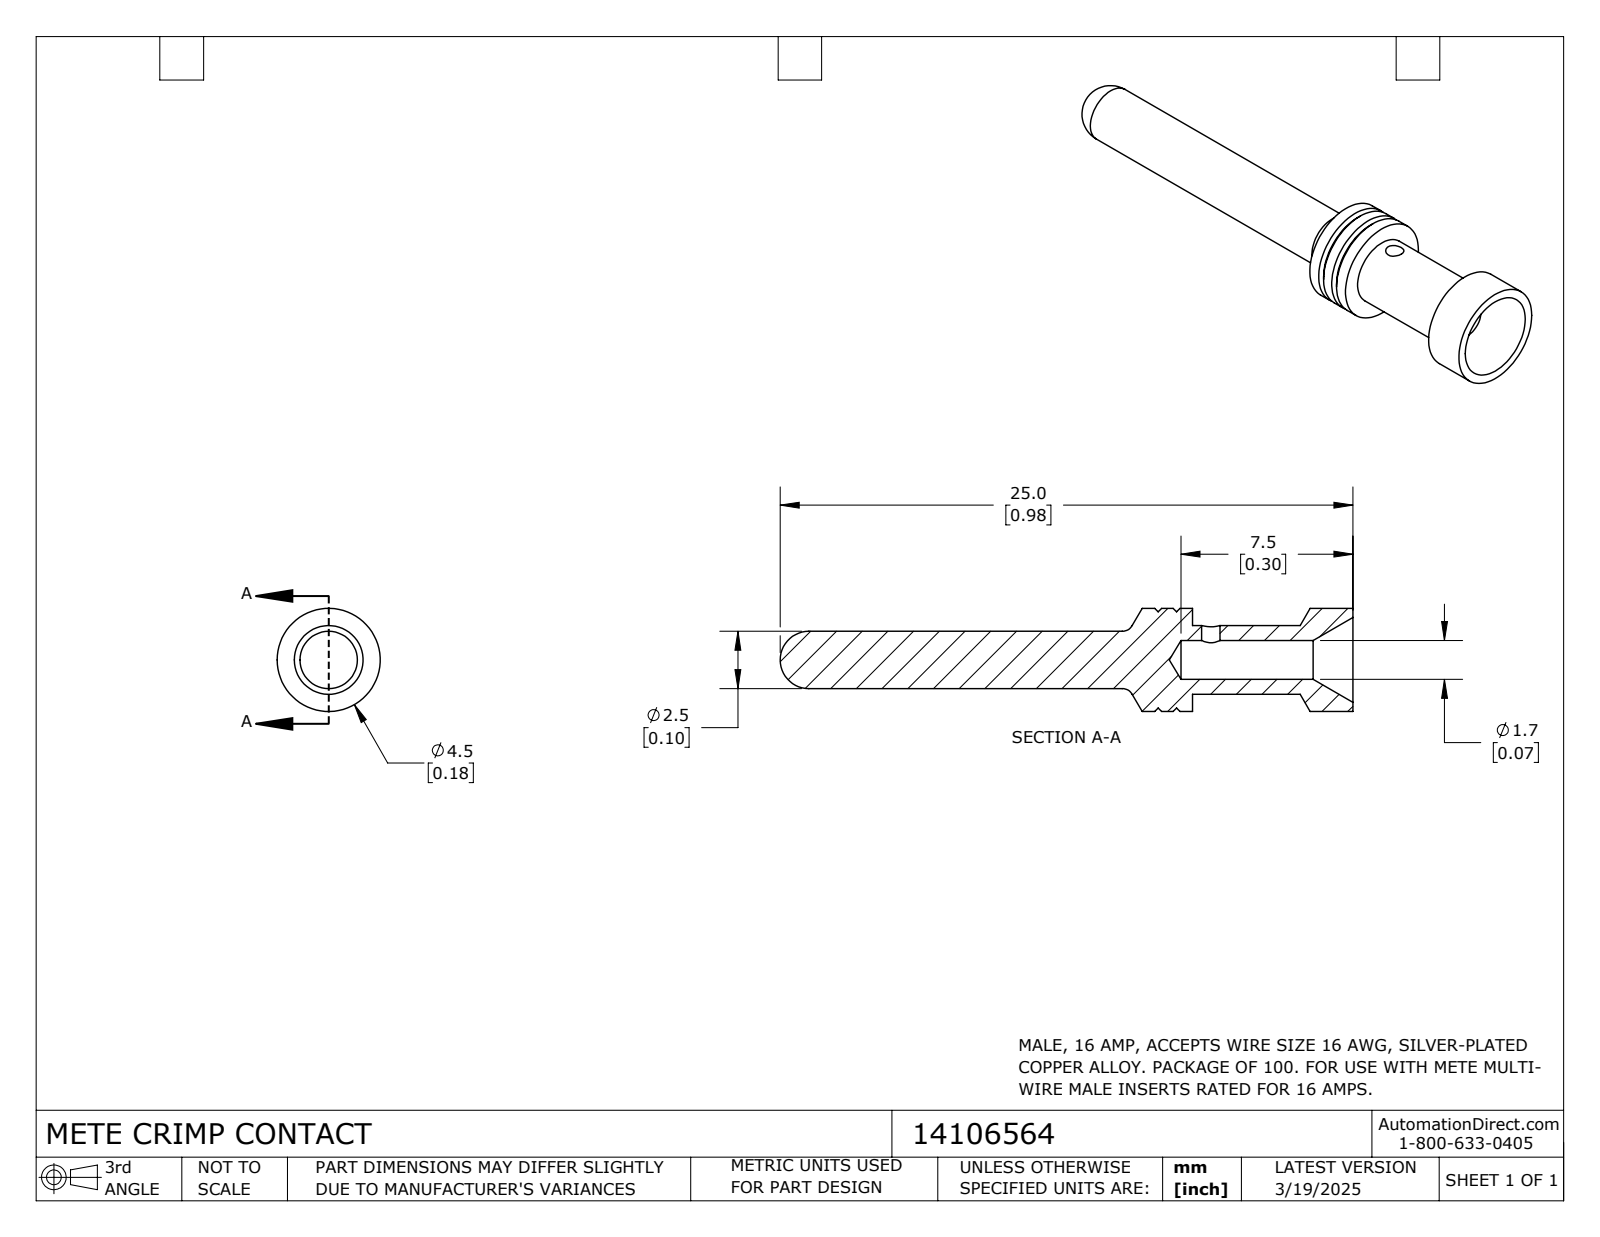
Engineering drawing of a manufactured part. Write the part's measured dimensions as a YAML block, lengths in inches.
part_name: "14106564"
step_written_by: "SolidWorks 2024 (CONFIG_CONTROL_DESIGN)"
units: inches
bodies: {solids: 1, faces: 38, planar: 2, cylindrical: 16, other: 20}
overall_size: [0.984, 0.177, 0.177]
volume: 0.01
surface_area: 0.484
round_holes:
  - {diameter: 0.031, count: 1}
  - {diameter: 0.067, count: 1}
round_bosses_or_shafts:
  - {diameter: 0.177, count: 1}
  - {diameter: 0.118, count: 1}
  - {diameter: 0.098, count: 1}
face_to_face_distances: [0.276]
